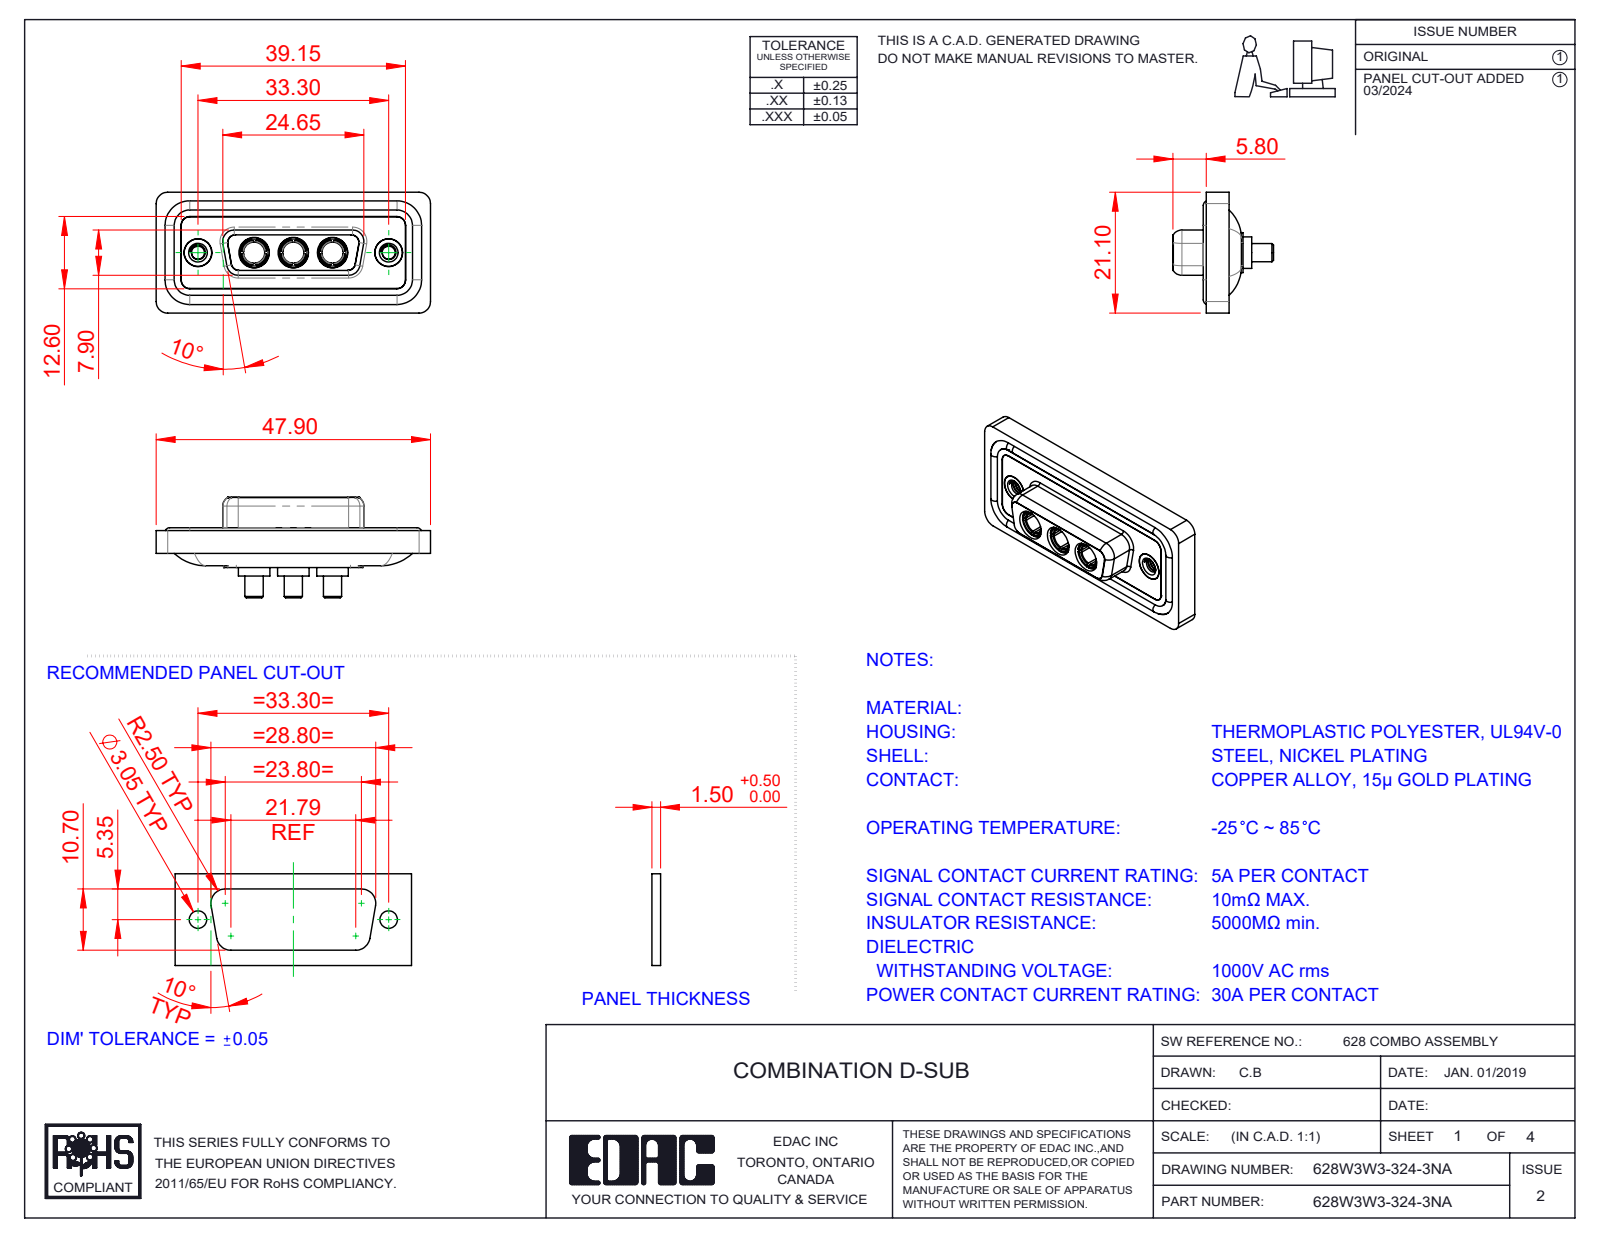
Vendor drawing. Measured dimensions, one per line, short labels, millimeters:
name: 628Combo Shell Front_15 Contacts; Power Socket_30A S; 628Combo Shell Rear_15 Contacts; 628Combo Threaded Rivet_A (+3 more)
written by: SolidWorks 2023 (CONFIG_CONTROL_DESIGN)
unit: mm
bodies: 13 solids, 606 faces (192 planar, 259 cylindrical, 155 other)
size: 47.9 × 21.1 × 17.55
volume: 6 049 mm³; area: 9 750 mm²
holes: 5× ⌀4.85, 3× ⌀3.7, 3× ⌀5.3, 2× ⌀2.26, 2× ⌀4, 2× ⌀4.05, 2× ⌀5
bosses: 4× ⌀1.6, 3× ⌀5.5, 3× ⌀5.2, 3× ⌀4.96, 3× ⌀4.75, 3× ⌀3.75, 3× ⌀3.2, 2× ⌀4.95
rounds: 22× R1.5, 20× R2, 12× R1.35, 8× R1.6, 4× R0.25, 4× R0.5, 4× R0.6, 4× R0.65
face distances: 0.4, 1.8, 1.6, 0.5, 7.45, 1.1, 2.9, 5.65, 7.05, 6.6
hole spacings: 6.85, 9.8, 16.65, 23.5, 13.7, 33.3
